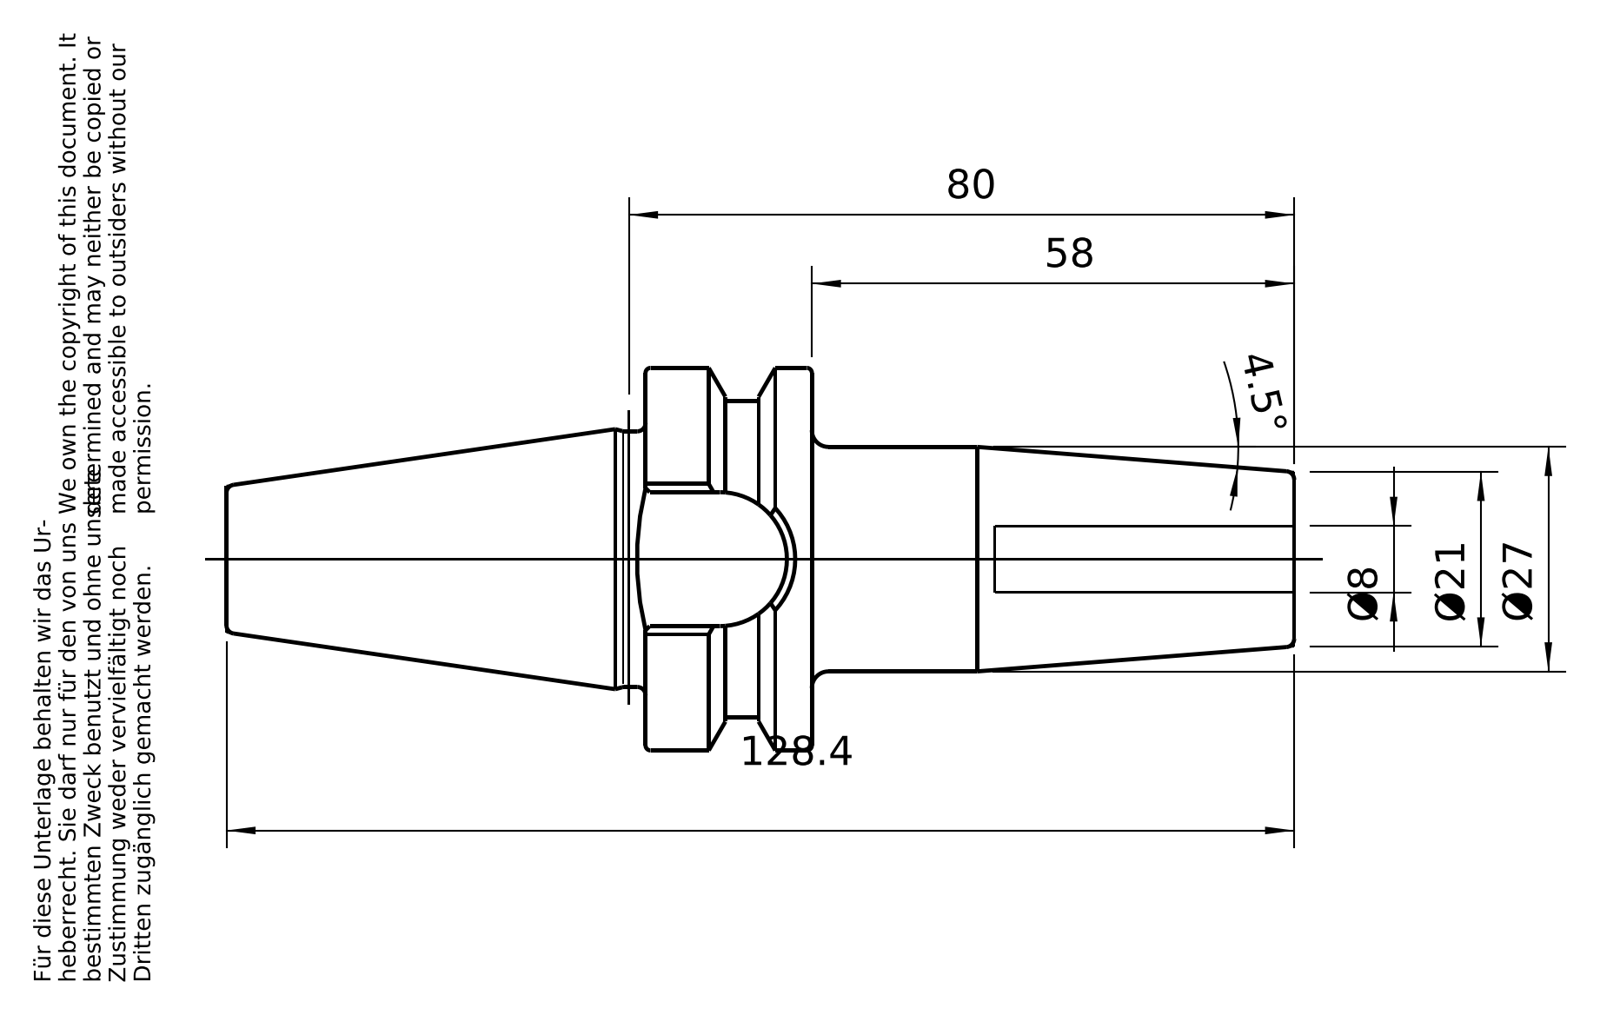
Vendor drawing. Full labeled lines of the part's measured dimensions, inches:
Part name (STEP PRODUCT): 30-640-08
STEP written by: PRO/ENGINEER BY PARAMETRIC TECHNOLOGY CORPORATION, 2010430 (CONFIG_CONTROL_DESIGN)
Units: inches
Bodies: 1 solid, 96 faces (26 planar, 22 cylindrical, 48 other)
Overall size (bounding box): 5.055 × 1.81 × 1.81
Volume: 4.668 in³ · Surface area: 26.35 in²
Round holes (diameter × count): ⌀0.315 ×1, ⌀0.398 ×1, ⌀0.493 ×1, ⌀0.512 ×1
Round bosses / shafts (diameter × count): ⌀1.81 ×1, ⌀1.211 ×1, ⌀1.063 ×1, ⌀0.473 ×1
Partial cylindrical surfaces — rounded edges, fillets, slot ends (radius × count): R0.319 ×1, R0.743 ×1
Main face-to-face distances: 0.787, 1.272, 3.071, 2.283, 0.638, 1.654, 0.866, 1.417, 1.984, 2.772
